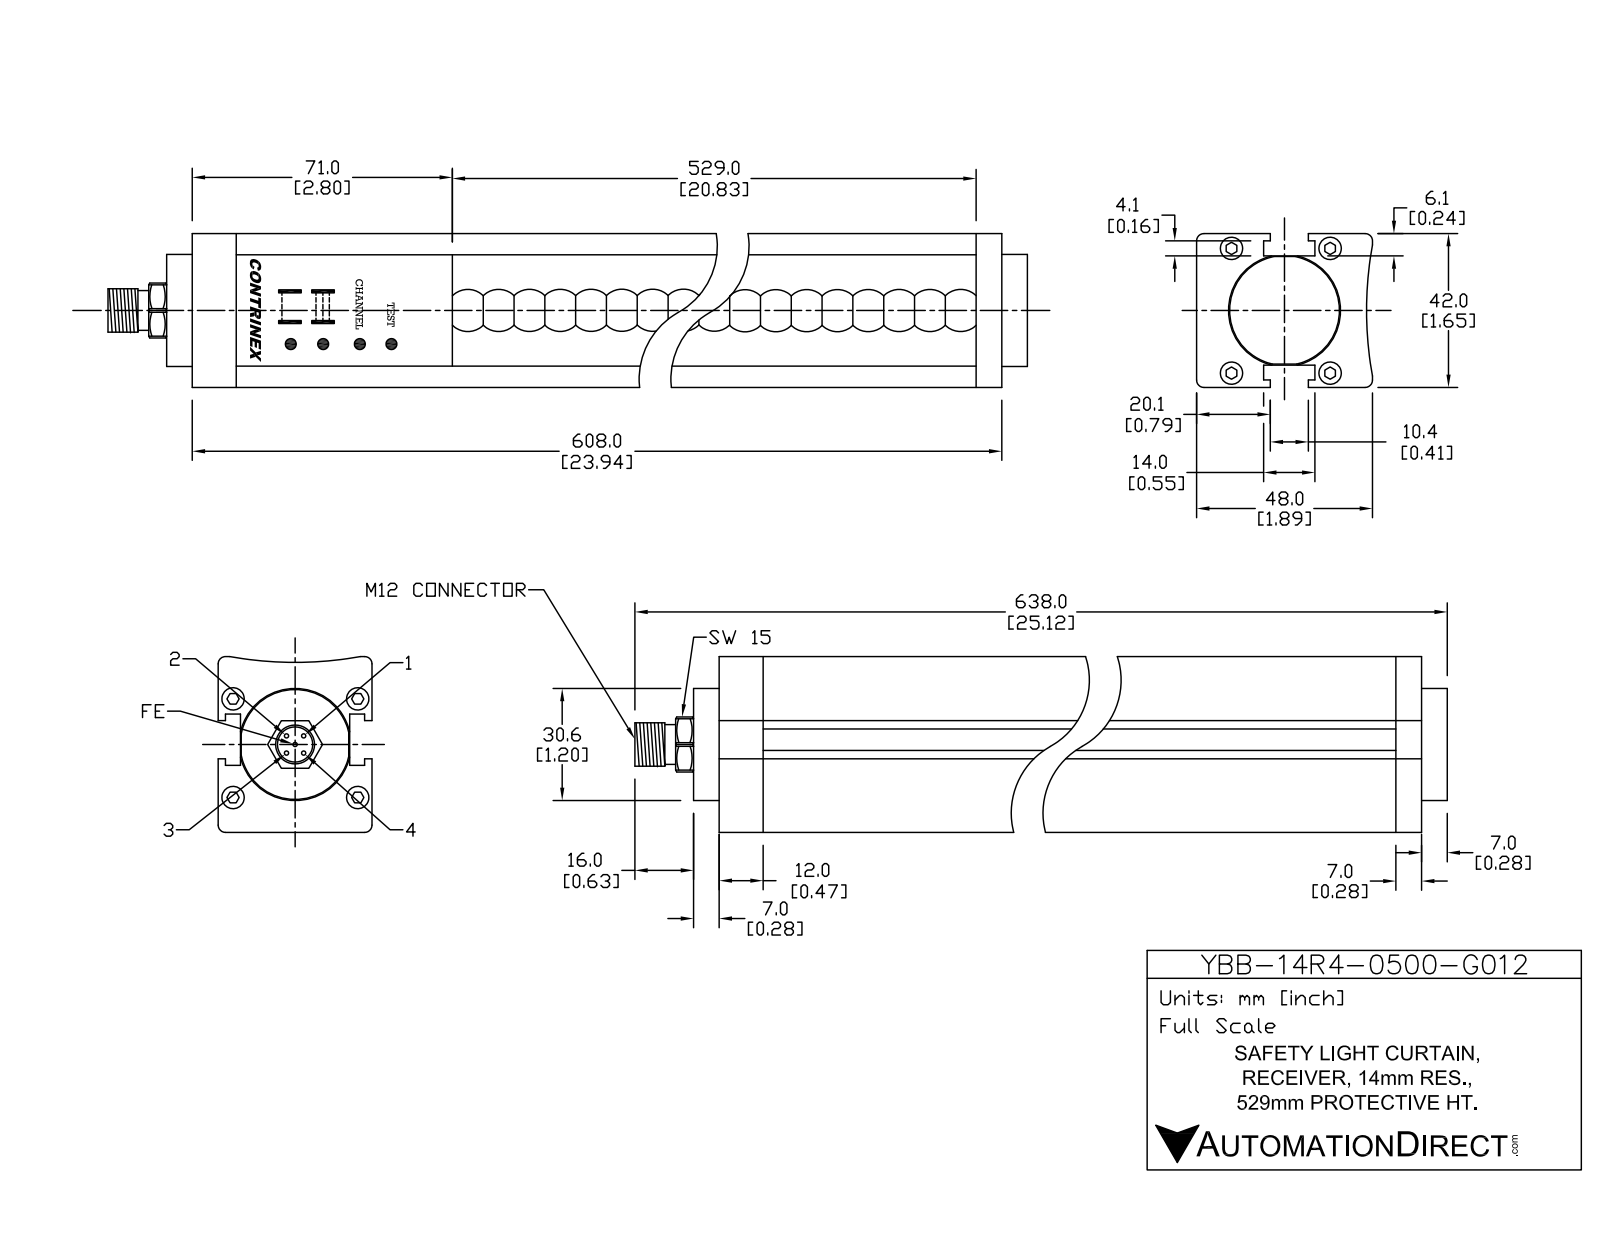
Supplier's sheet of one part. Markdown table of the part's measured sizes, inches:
| quantity | value |
| --- | --- |
| part name | YBB-14R4-0500-G012 |
| STEP written by | SolidWorks 2016 (AUTOMOTIVE_DESIGN) |
| units | inches |
| bodies | 19 solids, 440 faces (208 planar, 168 cylindrical, 64 other) |
| overall size | 25.118 × 1.89 × 1.654 |
| volume | 67.07 in³ |
| surface area | 228.5 in² |
| round holes (diameter × count) | 0.236 × 4, 0.335 × 1, 1.26 × 1 |
| round bosses / shafts (diameter × count) | 0.039 × 5, 0.217 × 4, 1.205 × 1, 0.472 × 1, 0.413 × 1 |
| partial cylindrical surfaces (radius × count) | 0.039 × 48, 0.02 × 4, 0.022 × 2, 0.323 × 1, 3.937 × 1 |
| main face-to-face distances | 0.248, 1.406, 1.654, 1.157, 0.551, 0.677, 1.228, 23.15, 0.618, 1.169 |
| hole center spacings | 0.828, 0.88, 1.059, 1.339, 1.707 |
